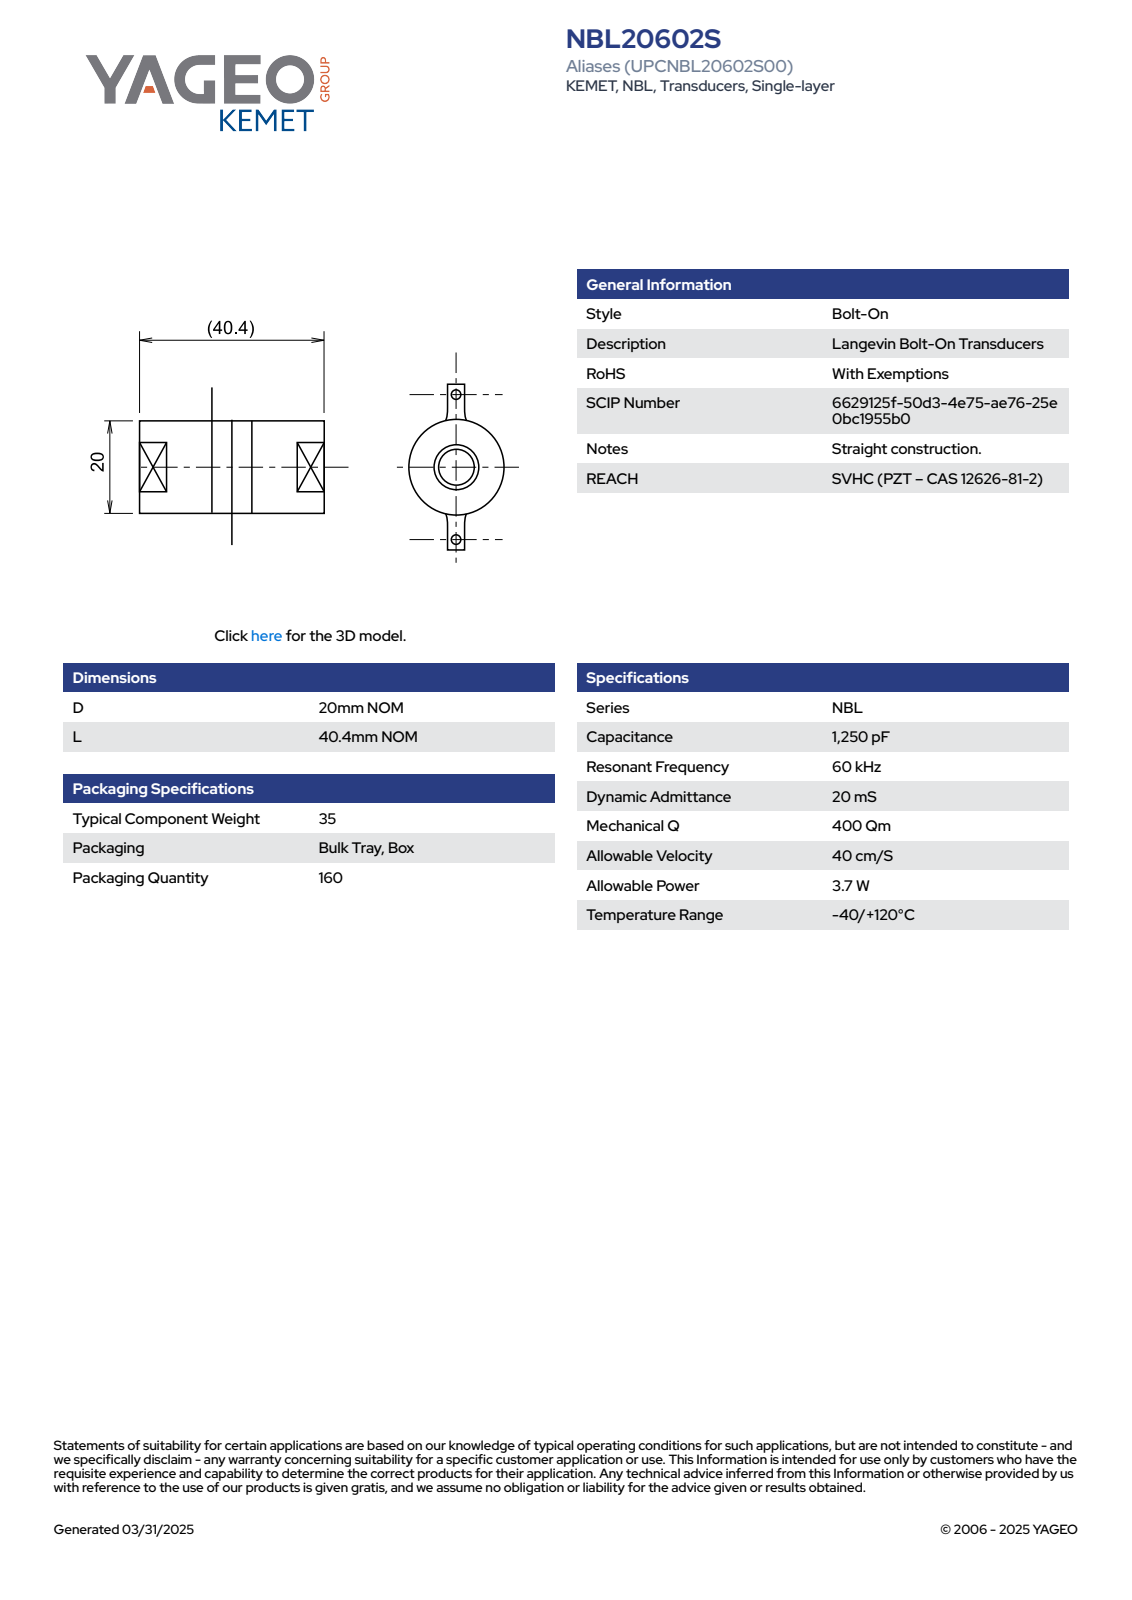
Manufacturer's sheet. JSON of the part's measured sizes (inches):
{"part_name": "ATB_20602S_D20L40.4", "step_written_by": "SolidWorks 2014 (AUTOMOTIVE_DESIGN)", "units": "inches", "bodies": {"solids": 3, "faces": 91, "planar": 77, "cylindrical": 14, "other": 0}, "overall_size": [1.591, 1.03, 0.787], "volume_in3": 0.759, "surface_area_in2": 5.909, "round_holes": [[0.039, 2]], "round_bosses_or_shafts": [[0.787, 1], [0.783, 1]], "face_to_face_distances": [0.793, 0.797, 1.591, 0.695, 0.201, 0.207, 0.528, 0.596, 0.994, 0.197], "hole_center_spacings": [0.905]}
